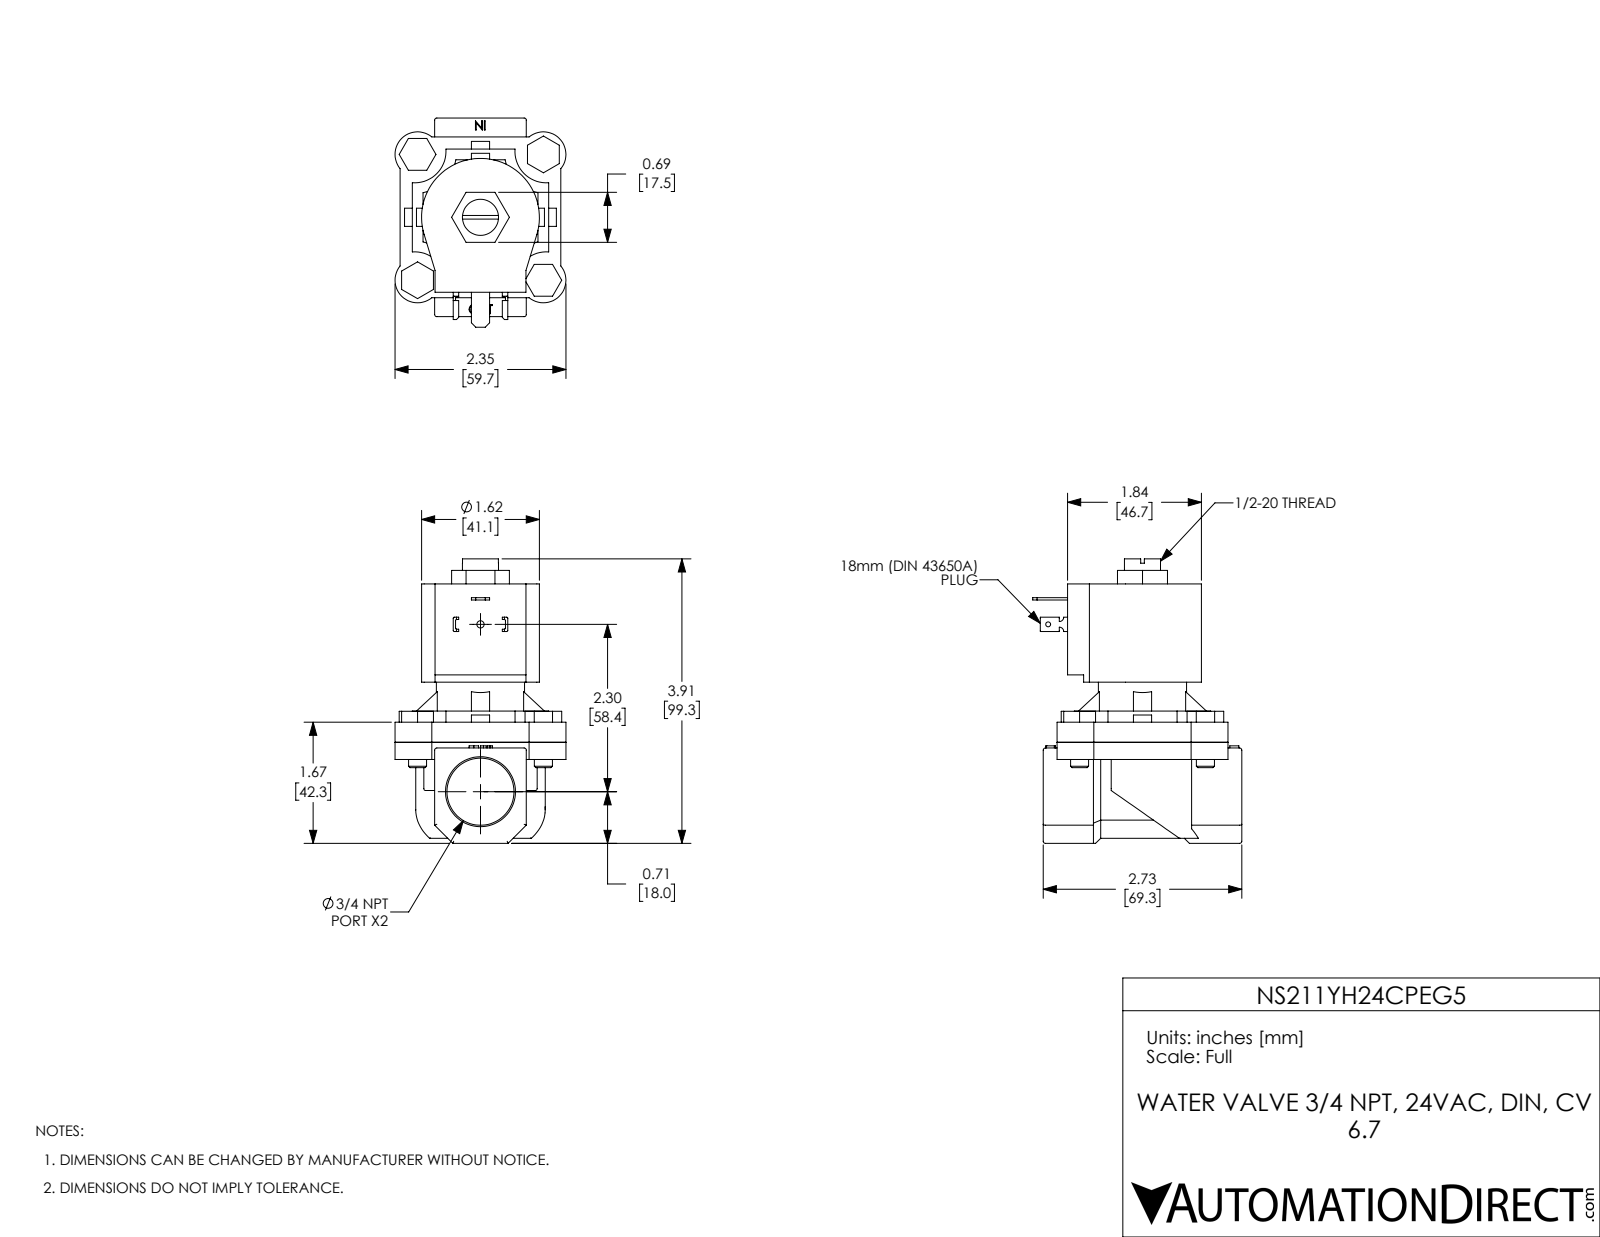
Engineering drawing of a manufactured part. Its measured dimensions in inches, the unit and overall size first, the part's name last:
Units: inches
Overall size (bounding box): 3.91 × 2.875 × 2.35
Round holes (diameter × count): ⌀0.25 ×4, ⌀0.067 ×1, ⌀0.1 ×1, ⌀0.496 ×1, ⌀0.512 ×1, ⌀0.922 ×1, ⌀1.155 ×1
Round bosses / shafts (diameter × count): ⌀0.248 ×4, ⌀1.213 ×1
Partial cylindrical surfaces — rounded edges, fillets, slot ends (radius × count): R0.03 ×15, R0.015 ×8, R0.31 ×4, R0.432 ×4, R0.579 ×4, R0.06 ×2, R0.81 ×1, R0.89 ×1
Main face-to-face distances: 0.276, 2.177, 1.901, 0.236, 0.512, 2.413, 1.063, 0.827, 0.551, 1.35
Hole centre spacings: 1.223, 1.73, 2.446, 2.3
Volume: 9.997 in³ · Surface area: 68.35 in²
Bodies: 11 solids, 387 faces (241 planar, 113 cylindrical, 33 other)
Part name (STEP PRODUCT): NS211YH24CPEG5
STEP written by: SolidWorks 2024 (CONFIG_CONTROL_DESIGN)
